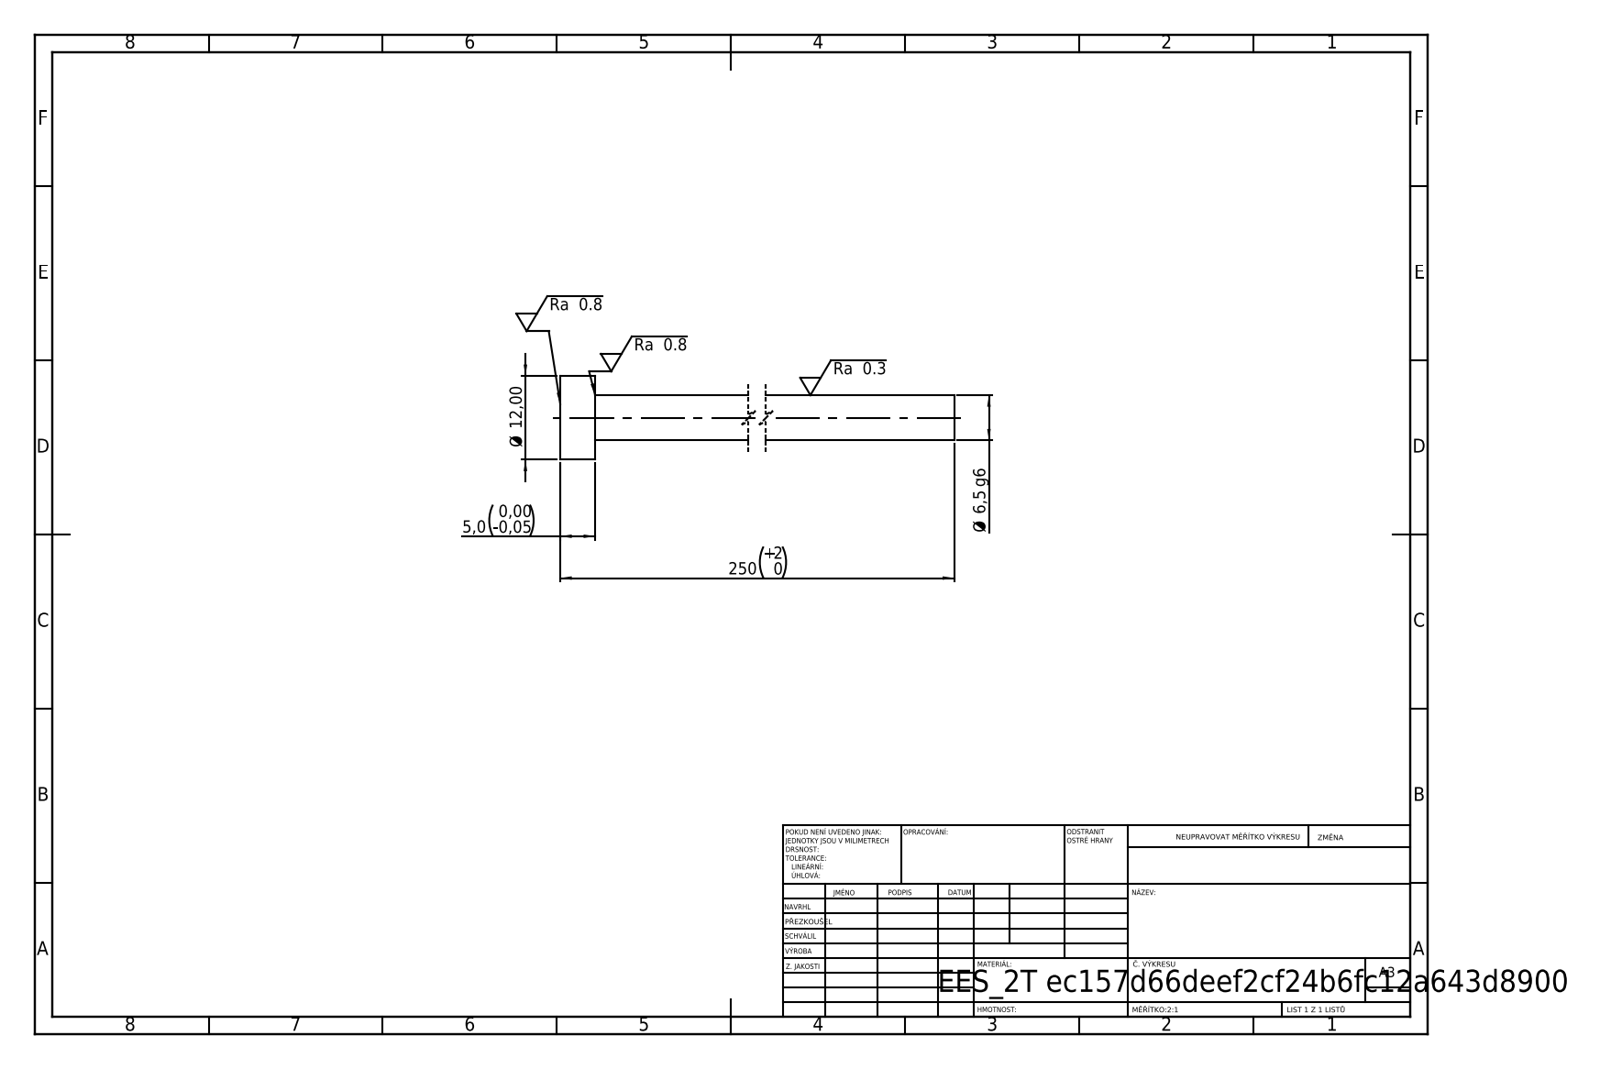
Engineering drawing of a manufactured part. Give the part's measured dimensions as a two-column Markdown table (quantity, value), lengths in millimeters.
| quantity | value |
| --- | --- |
| STEP written by | SolidWorks 2019 (CONFIG_CONTROL_DESIGN) |
| units | millimeters |
| bodies | 1 solid, 7 faces (3 planar, 4 cylindrical, 0 other) |
| overall size | 250 × 12 × 12 |
| volume | 8 695 mm³ |
| surface area | 5 418 mm² |
| round bosses / shafts (diameter × count) | 12 × 1, 6.5 × 1 |
| main face-to-face distances | 5, 250, 245 |
